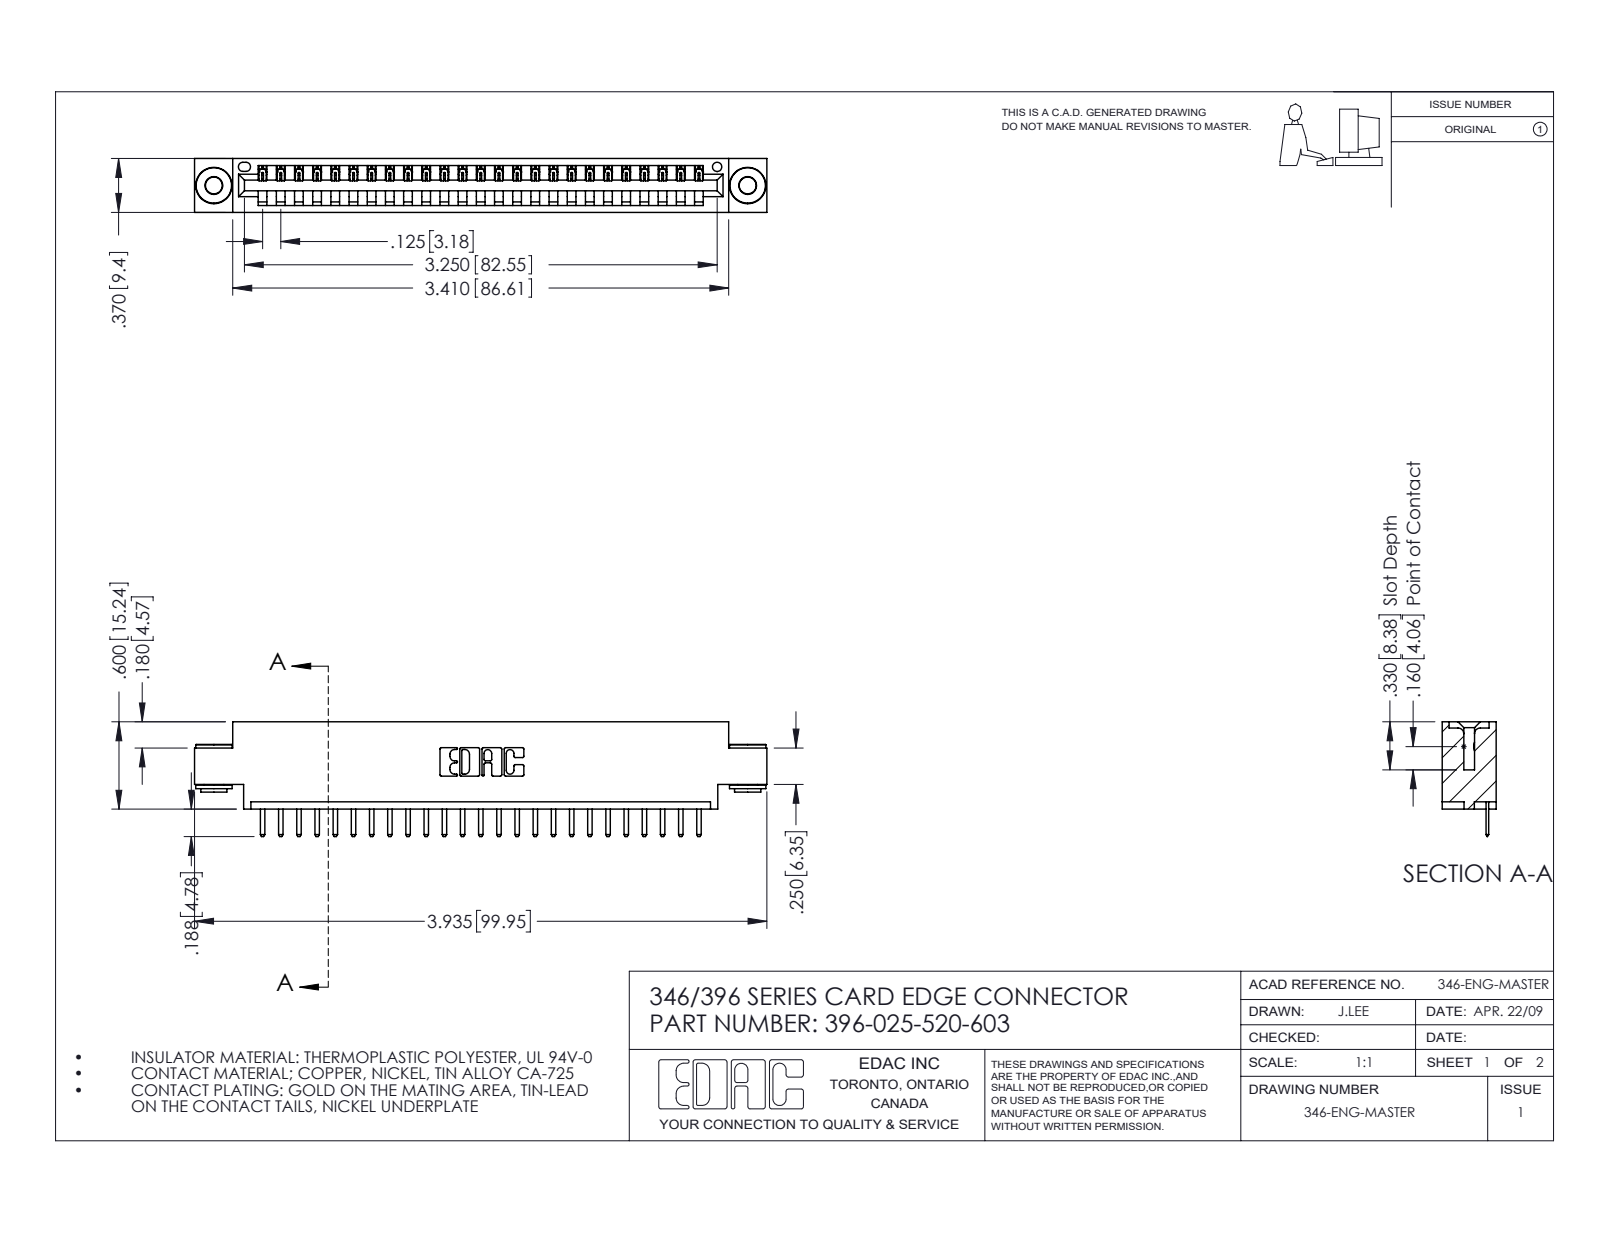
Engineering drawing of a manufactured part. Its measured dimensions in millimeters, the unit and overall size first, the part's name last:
Units: millimetres
Overall size (bounding box): 99.9 × 20 × 9.4
Round holes (diameter × count): ⌀2.9 ×2, ⌀4 ×2, ⌀1.6 ×1
Round bosses / shafts (diameter × count): ⌀6.4 ×2, ⌀4.6 ×2, ⌀3.5 ×2
Partial cylindrical surfaces — rounded edges, fillets, slot ends (radius × count): R0.3 ×52, R0.2 ×50, R0.3 ×22, R0.2 ×6, R0.8 ×6, R0.7 ×3, R0.8 ×2, R1 ×2
Main face-to-face distances: 9.4, 1.2, 8.2, 6.4, 0.6, 3.8, 5.6, 2.5, 4.4, 1.8
Hole centre spacings: 6.2, 87.9, 93.2
Volume: 9 240 mm³ · Surface area: 11 510 mm²
Bodies: 28 solids, 1714 faces (1140 planar, 566 cylindrical, 8 other)
Part name (STEP PRODUCT): 396-025-520-603; 345-292-001_345-293-120; 345-250-002_345-250-002-102; 346 Part_0.170 Offset - 0.156 Dia-TH
STEP written by: SolidWorks 2016 (CONFIG_CONTROL_DESIGN)
